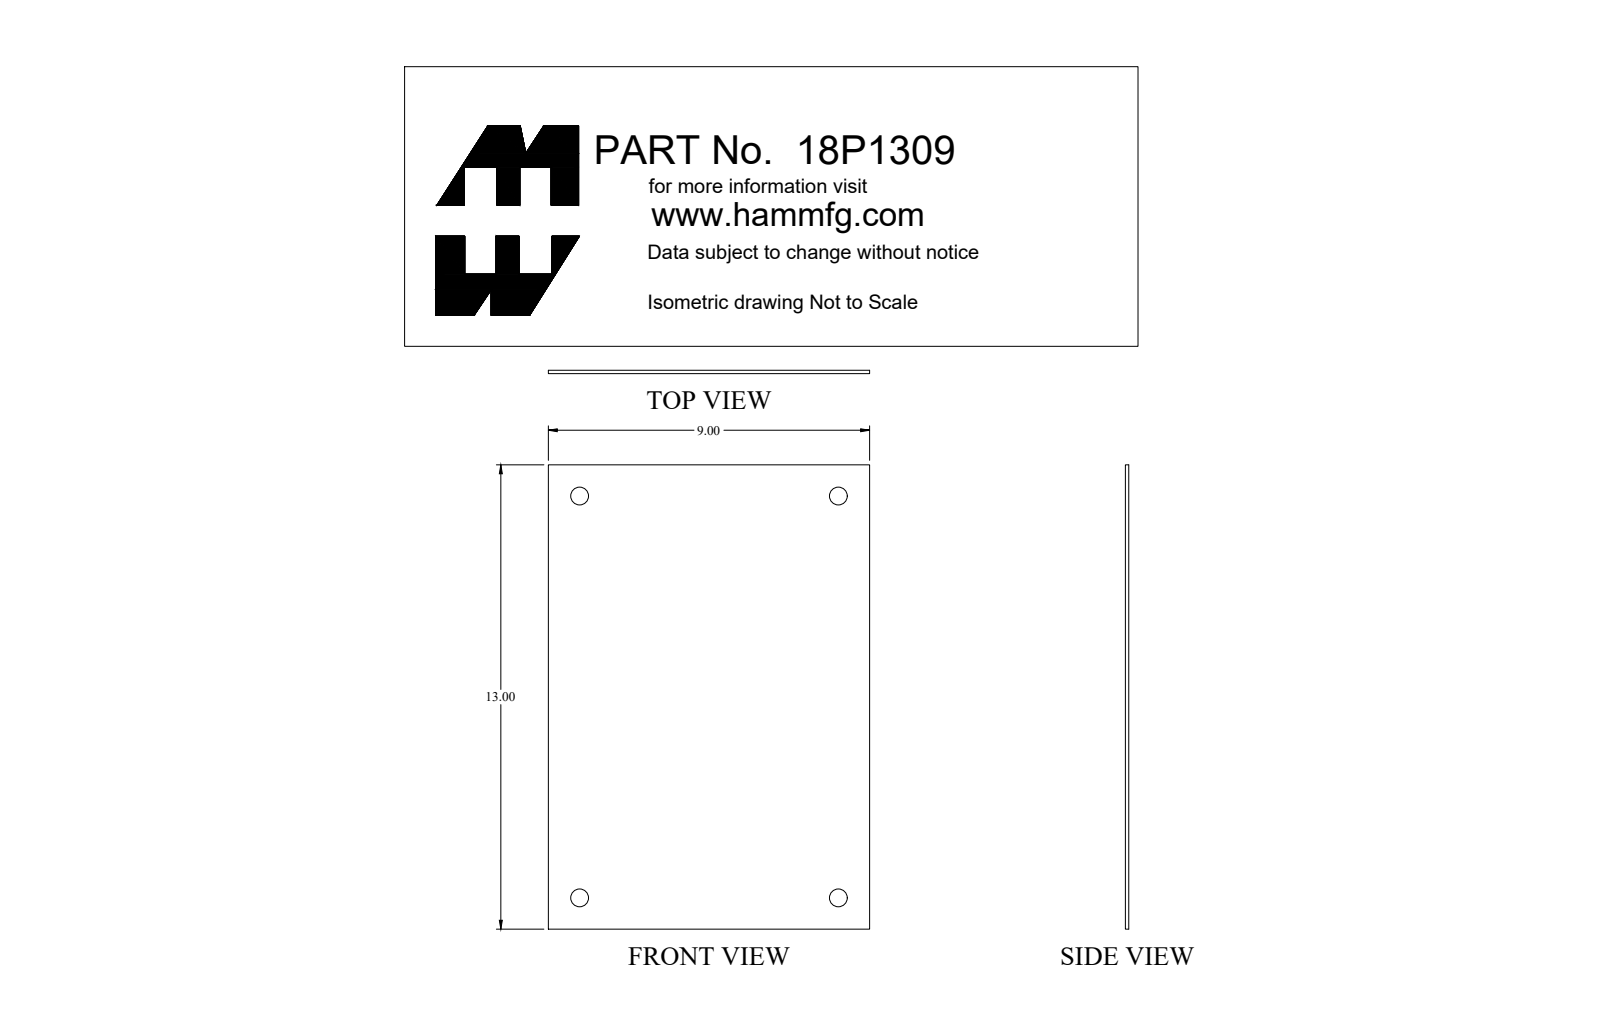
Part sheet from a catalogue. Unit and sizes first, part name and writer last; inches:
Units: inches
Overall size (bounding box): 13 × 9 × 0.095
Round holes (diameter × count): ⌀0.5 ×4
Main face-to-face distances: 0.095, 9, 13
Hole centre spacings: 7.25, 11.25, 13.384
Volume: 11.04 in³ · Surface area: 237.2 in²
Bodies: 1 solid, 14 faces (6 planar, 8 cylindrical, 0 other)
Part name (STEP PRODUCT): 18P1309_Default
STEP written by: SolidWorks 2018 (CONFIG_CONTROL_DESIGN)
